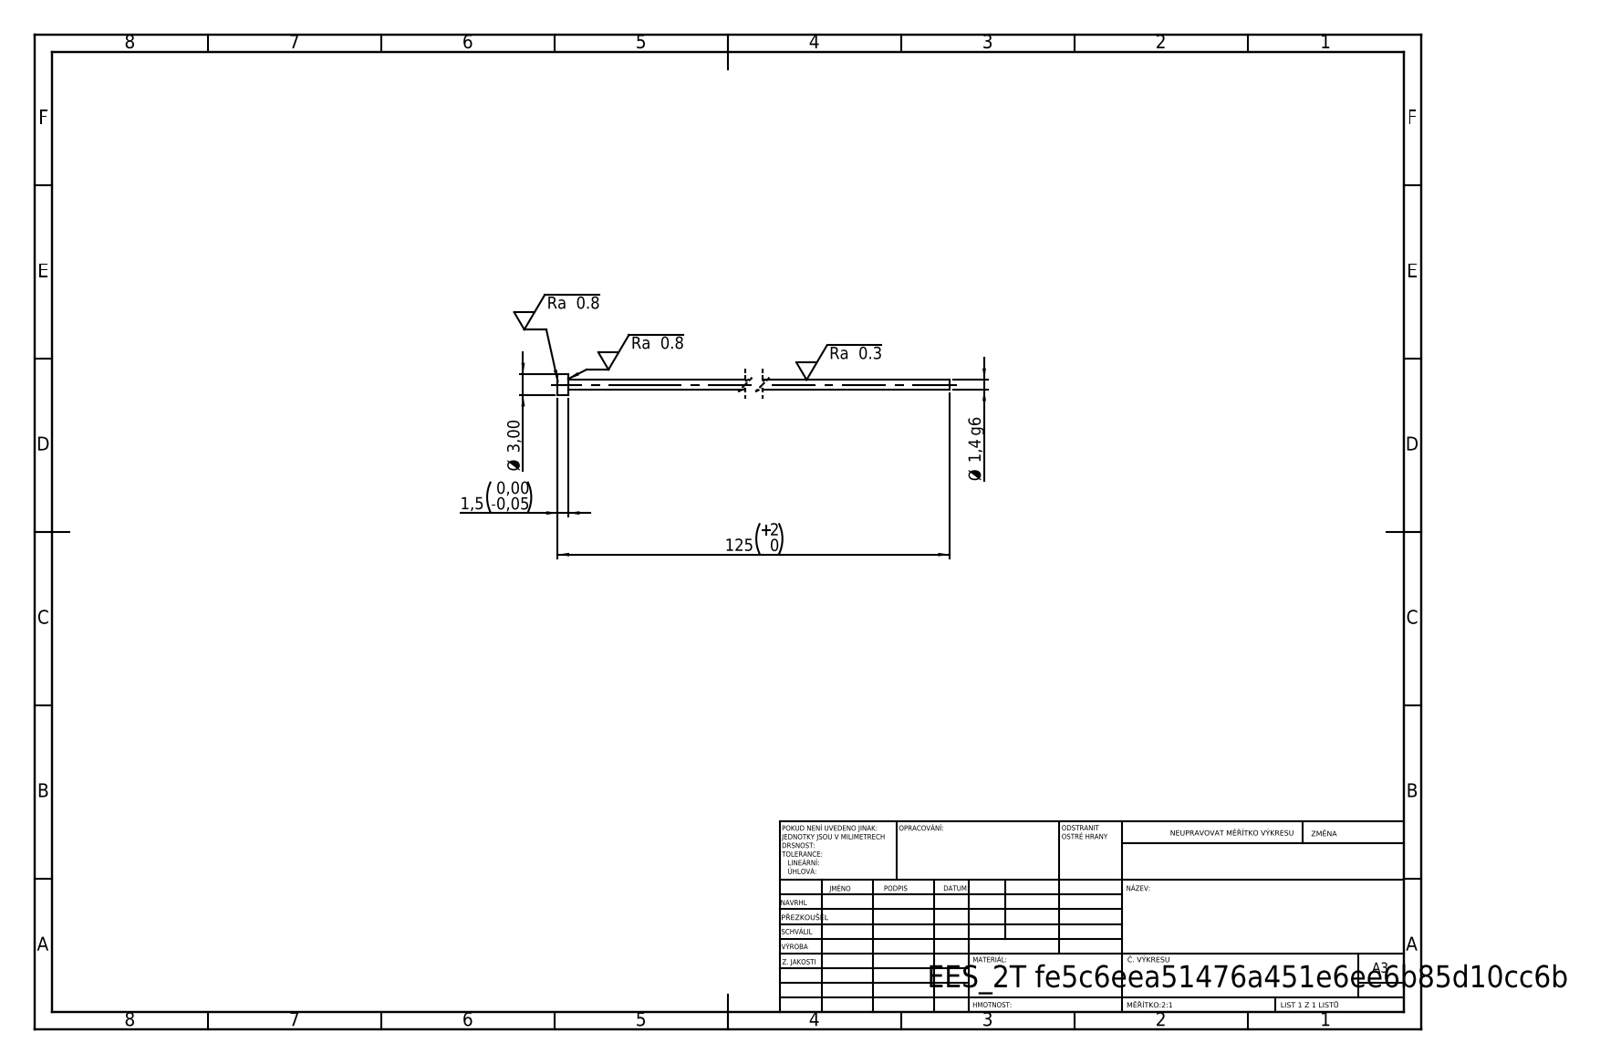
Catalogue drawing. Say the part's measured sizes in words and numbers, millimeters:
Its 3-D file was written by "SolidWorks 2019 (CONFIG_CONTROL_DESIGN)". It is 1 solid with 7 faces: 3 planar, 4 cylindrical and 0 other. Overall it measures 125 by 3 by 3 millimeters. Its volume is 201 cubic millimeters and its surface area 571 square millimeters. Round bosses or shafts: 1 of diameter 3, 1 of diameter 1.4. The main face-to-face distances are 1.5, 125, 123.5.
